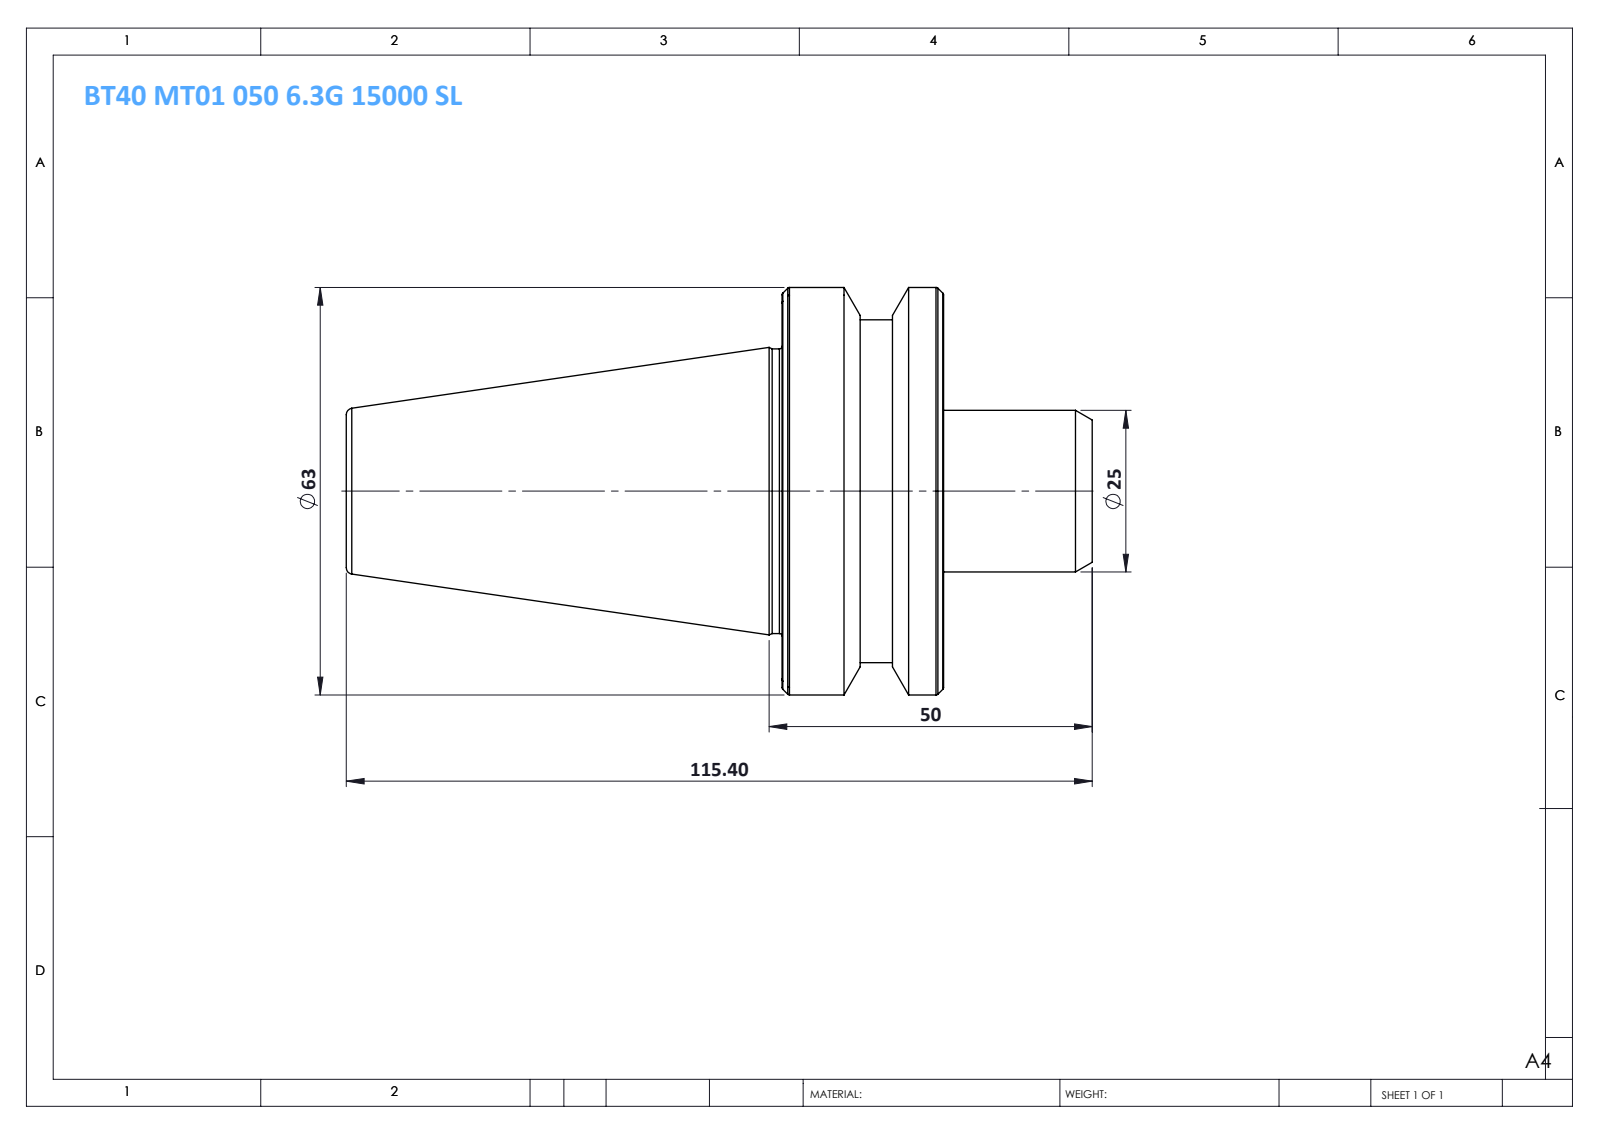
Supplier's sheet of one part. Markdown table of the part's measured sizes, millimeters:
| quantity | value |
| --- | --- |
| part name | BT40 MT01 050 6.3G 15000 SL |
| STEP written by | SolidWorks 2014 (CONFIG_CONTROL_DESIGN) |
| units | millimeters |
| bodies | 1 solid, 48 faces (6 planar, 10 cylindrical, 32 other) |
| overall size | 115.4 × 63 × 63 |
| volume | 149 490 mm³ |
| surface area | 20 041 mm² |
| round bosses / shafts (diameter × count) | 63 × 1, 53 × 1, 44 × 1, 25 × 1 |
| main face-to-face distances | 25, 92.4, 67.4, 23, 48, 115.4, 30.9, 7.9, 17.1, 84.5 |
